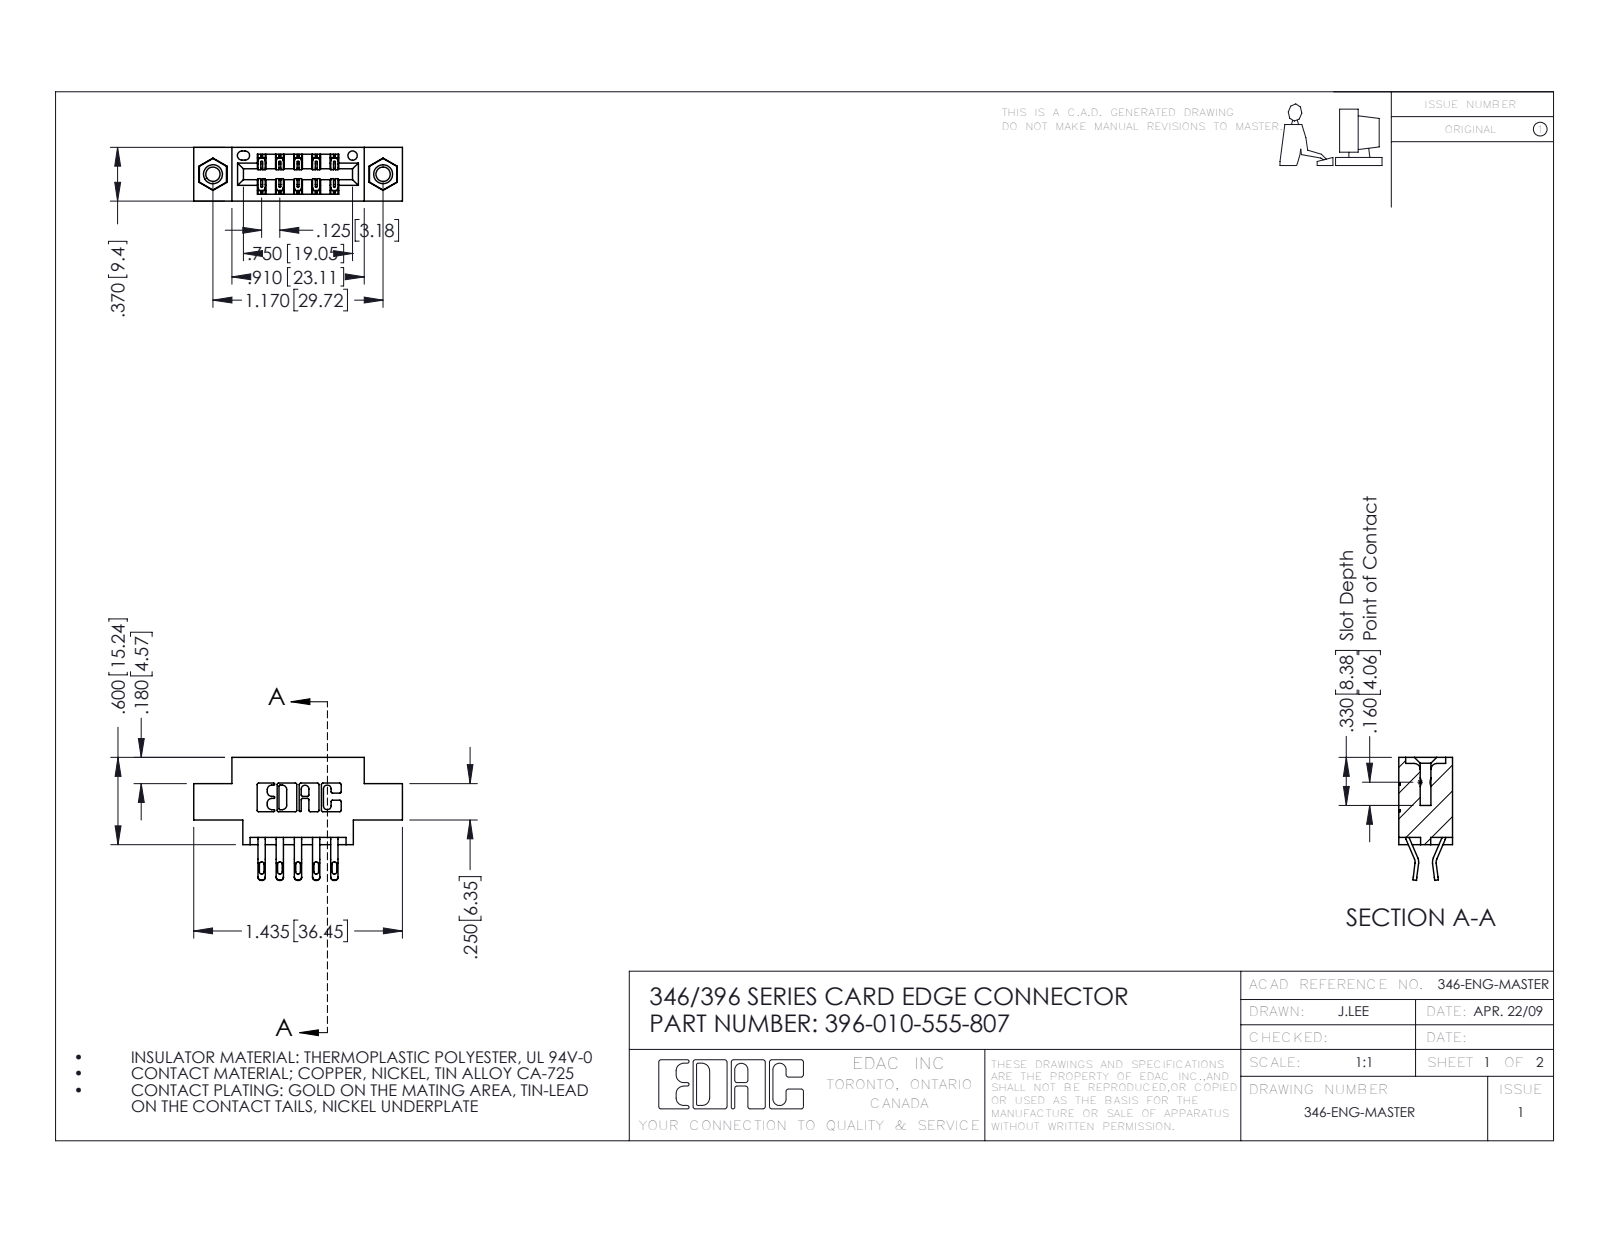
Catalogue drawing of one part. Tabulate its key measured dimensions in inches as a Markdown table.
| quantity | value |
| --- | --- |
| part name | 396-010-555-807; 346 Part_0.170 Offset - 0.156 Dia-TI; 345-292-001_555 Tail; 345-250-001_345-250-005-103 |
| STEP written by | SolidWorks 2016 (CONFIG_CONTROL_DESIGN) |
| units | inches |
| bodies | 13 solids, 766 faces (442 planar, 308 cylindrical, 16 other) |
| overall size | 1.435 × 0.845 × 0.37 |
| volume | 0.191 in³ |
| surface area | 6.253 in² |
| round holes (diameter × count) | 0.098 × 2, 0.125 × 2, 0.156 × 2, 0.064 × 1 |
| round bosses / shafts (diameter × count) | 0.155 × 2 |
| partial cylindrical surfaces (radius × count) | 0.01 × 22, 0.016 × 20, 0.02 × 20, 0.006 × 15, 0.007 × 6, 0.031 × 6, 0.026 × 3, 0.01 × 2 |
| main face-to-face distances | 0.37, 0.25, 0.048, 0.322, 0.222, 0.148, 0.125, 0.1, 0.174, 0.025 |
| hole center spacings | 0.246, 0.969, 1.17 |
